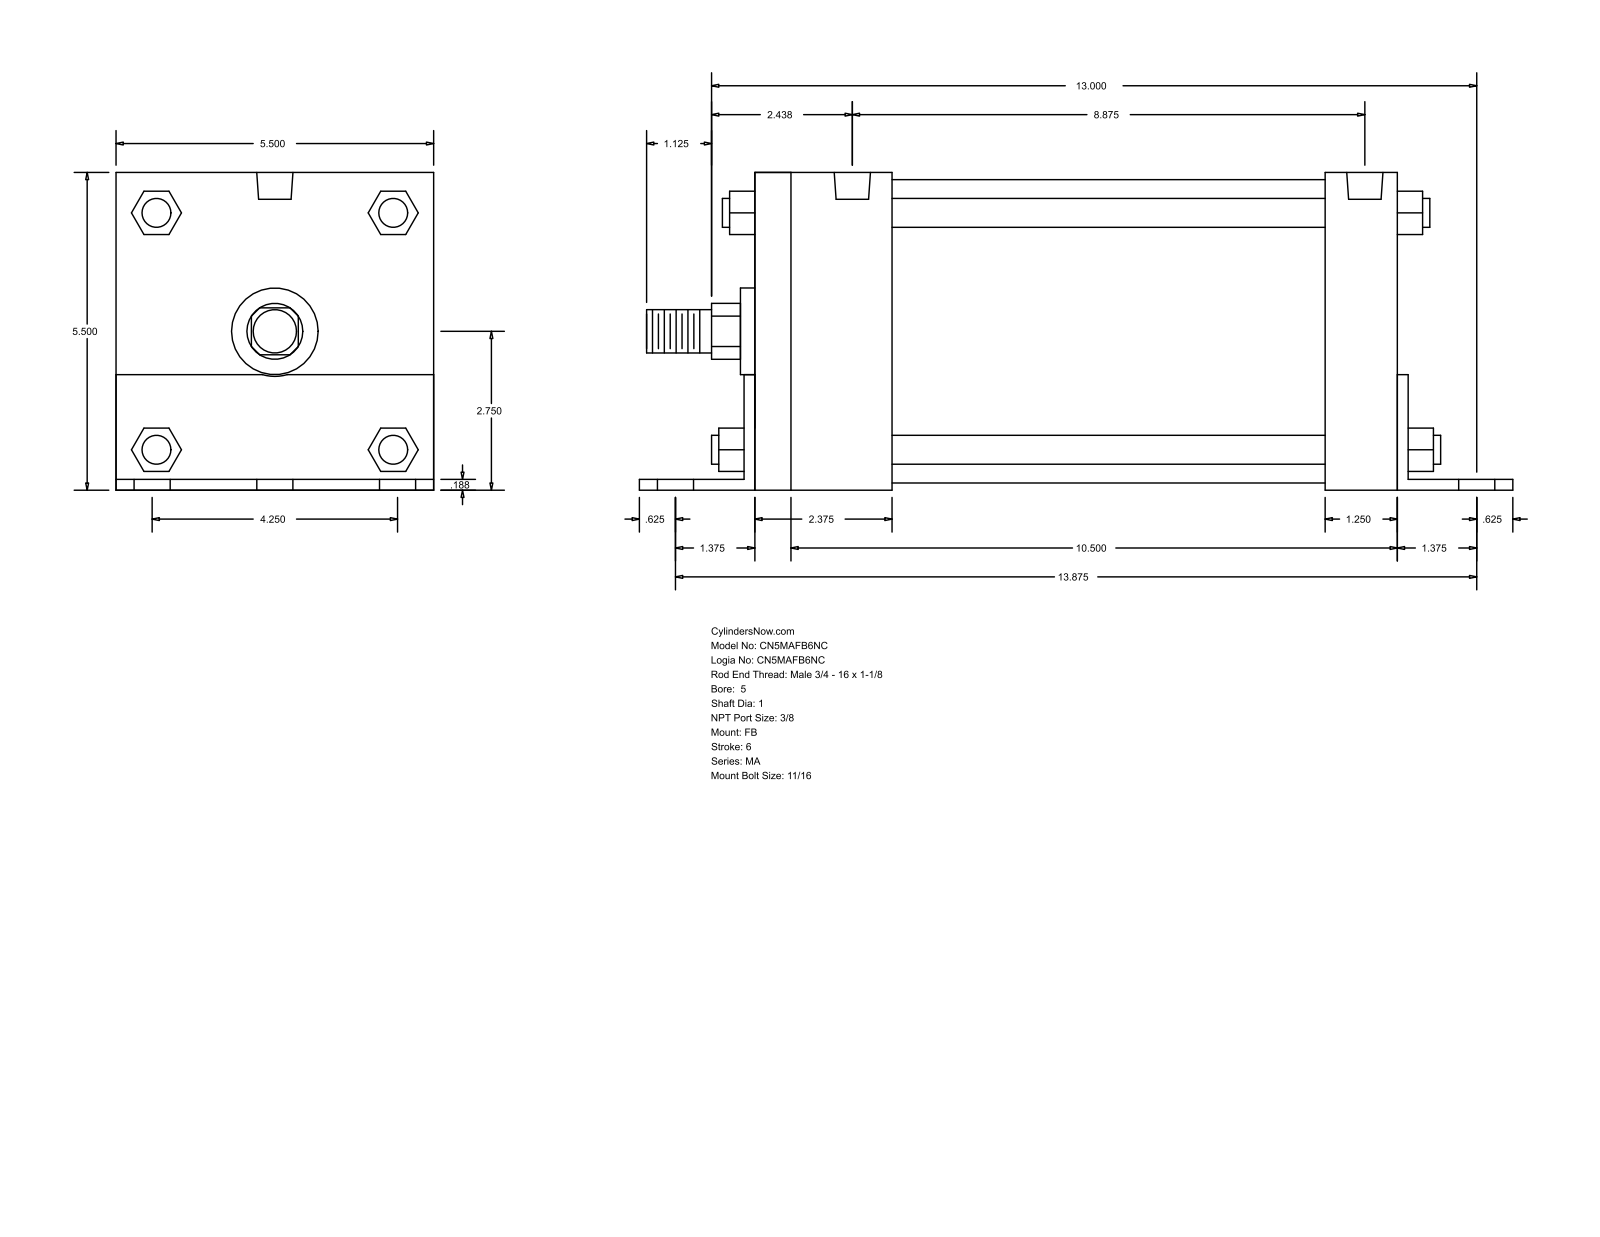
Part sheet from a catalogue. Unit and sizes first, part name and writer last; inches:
Units: inches
Overall size (bounding box): 15.125 × 5.502 × 5.5
Round holes (diameter × count): ⌀0.687 ×6, ⌀0.437 ×4, ⌀0.627 ×2
Round bosses / shafts (diameter × count): ⌀0.5 ×4, ⌀5.25 ×1, ⌀1.5 ×1, ⌀1 ×1, ⌀0.75 ×1
Partial cylindrical surfaces — rounded edges, fillets, slot ends (radius × count): R0.484 ×1, R0.78 ×1
Main face-to-face distances: 5.5, 0.187, 5.502, 0.185, 5.315, 11.125, 0.188, 11.313, 11.312, 11.5
Hole centre spacings: 2.125, 14.037, 13.875, 2.876, 3.006, 3.728, 3.883, 4.25
Bodies: 0 solids, 140 faces (105 planar, 35 cylindrical, 0 other)
Part name (STEP PRODUCT): MA_FB__0500_1
STEP written by: GSSL Pune (CONFIG_CONTROL_DESIGN)
